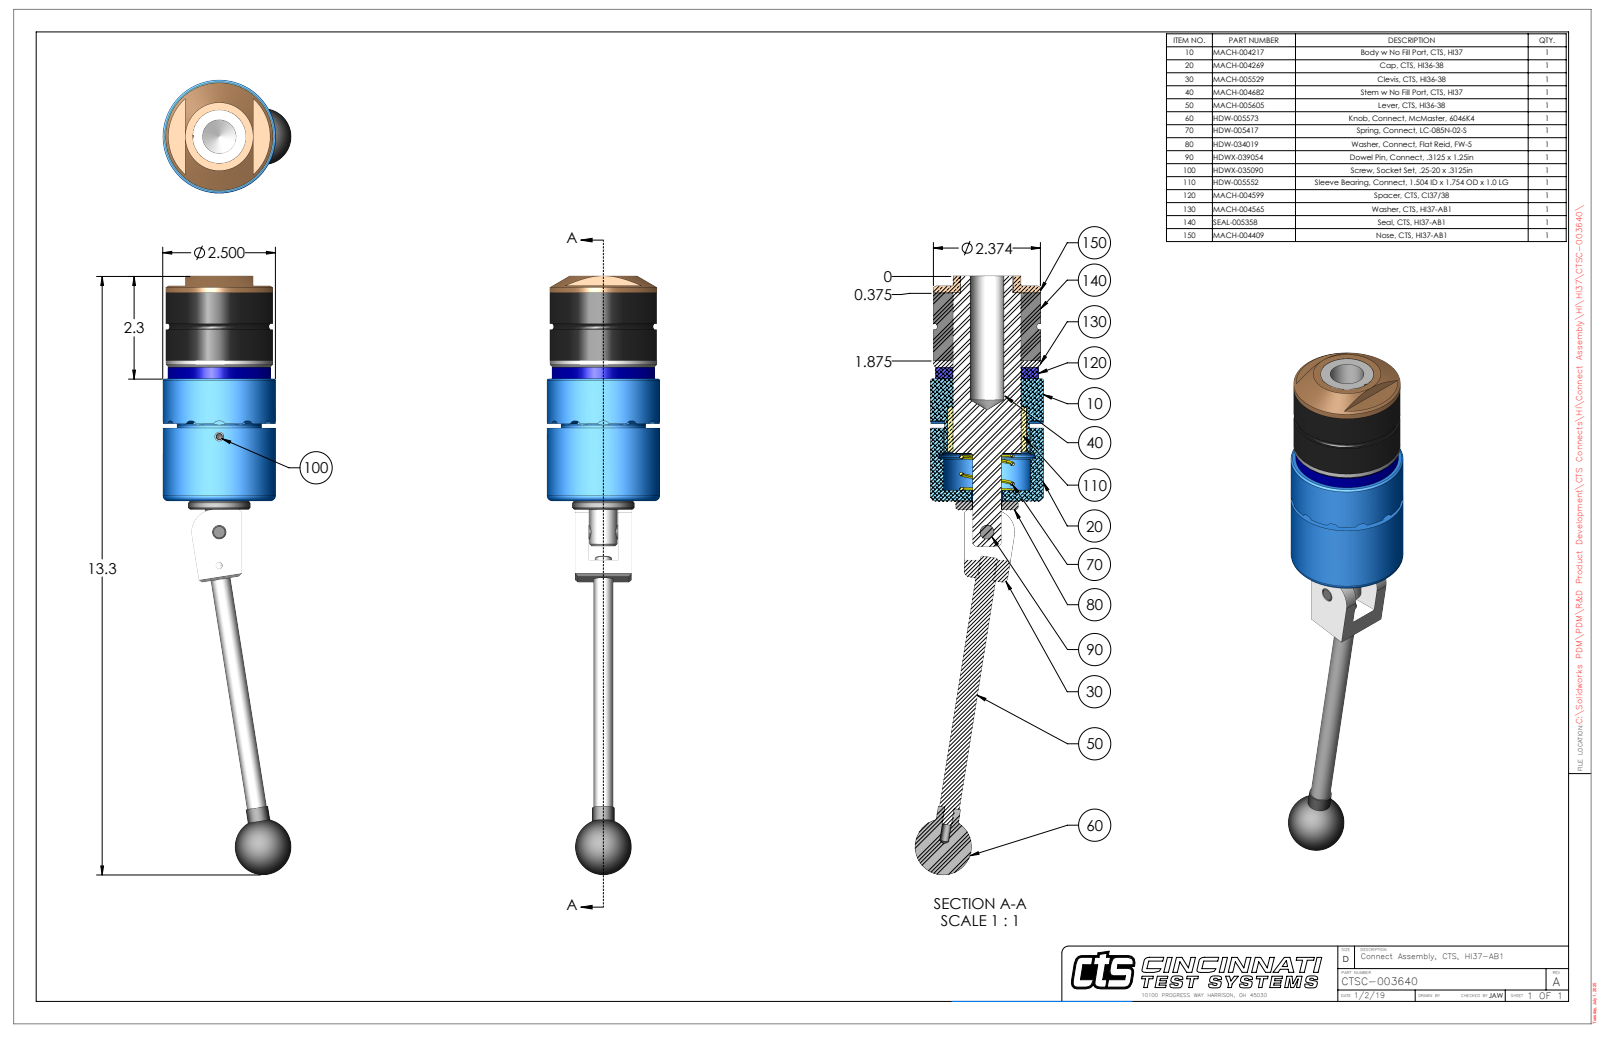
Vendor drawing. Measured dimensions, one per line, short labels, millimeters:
name: CTSC-003640
written by: SolidWorks 2023 (AUTOMOTIVE_DESIGN)
unit: mm
bodies: 10 solids, 288 faces (103 planar, 112 cylindrical, 73 other)
size: 337.2 × 72.2 × 63.5
volume: 407 900 mm³; area: 86 900 mm²
holes: 2× ⌀5.1, 1× ⌀3.8, 1× ⌀7.9, 1× ⌀8, 1× ⌀8, 1× ⌀16.7, 1× ⌀17.7, 1× ⌀19.1, 1× ⌀29.8, 1× ⌀38, 1× ⌀38.1, 1× ⌀38.4
bosses: 1× ⌀63.5, 1× ⌀60.3, 1× ⌀57.9, 1× ⌀47.6, 1× ⌀38.1, 1× ⌀38, 1× ⌀35.1, 1× ⌀31.8
rounds: 12× R3, 2× R0.7, 1× R12.7, 1× R29.5
face distances: 38.1, 10.2, 48.3, 68.9, 6.4, 79.1, 117.2, 75.3, 3.9, 42
hole spacings: 18.8, 53.8, 72.6
